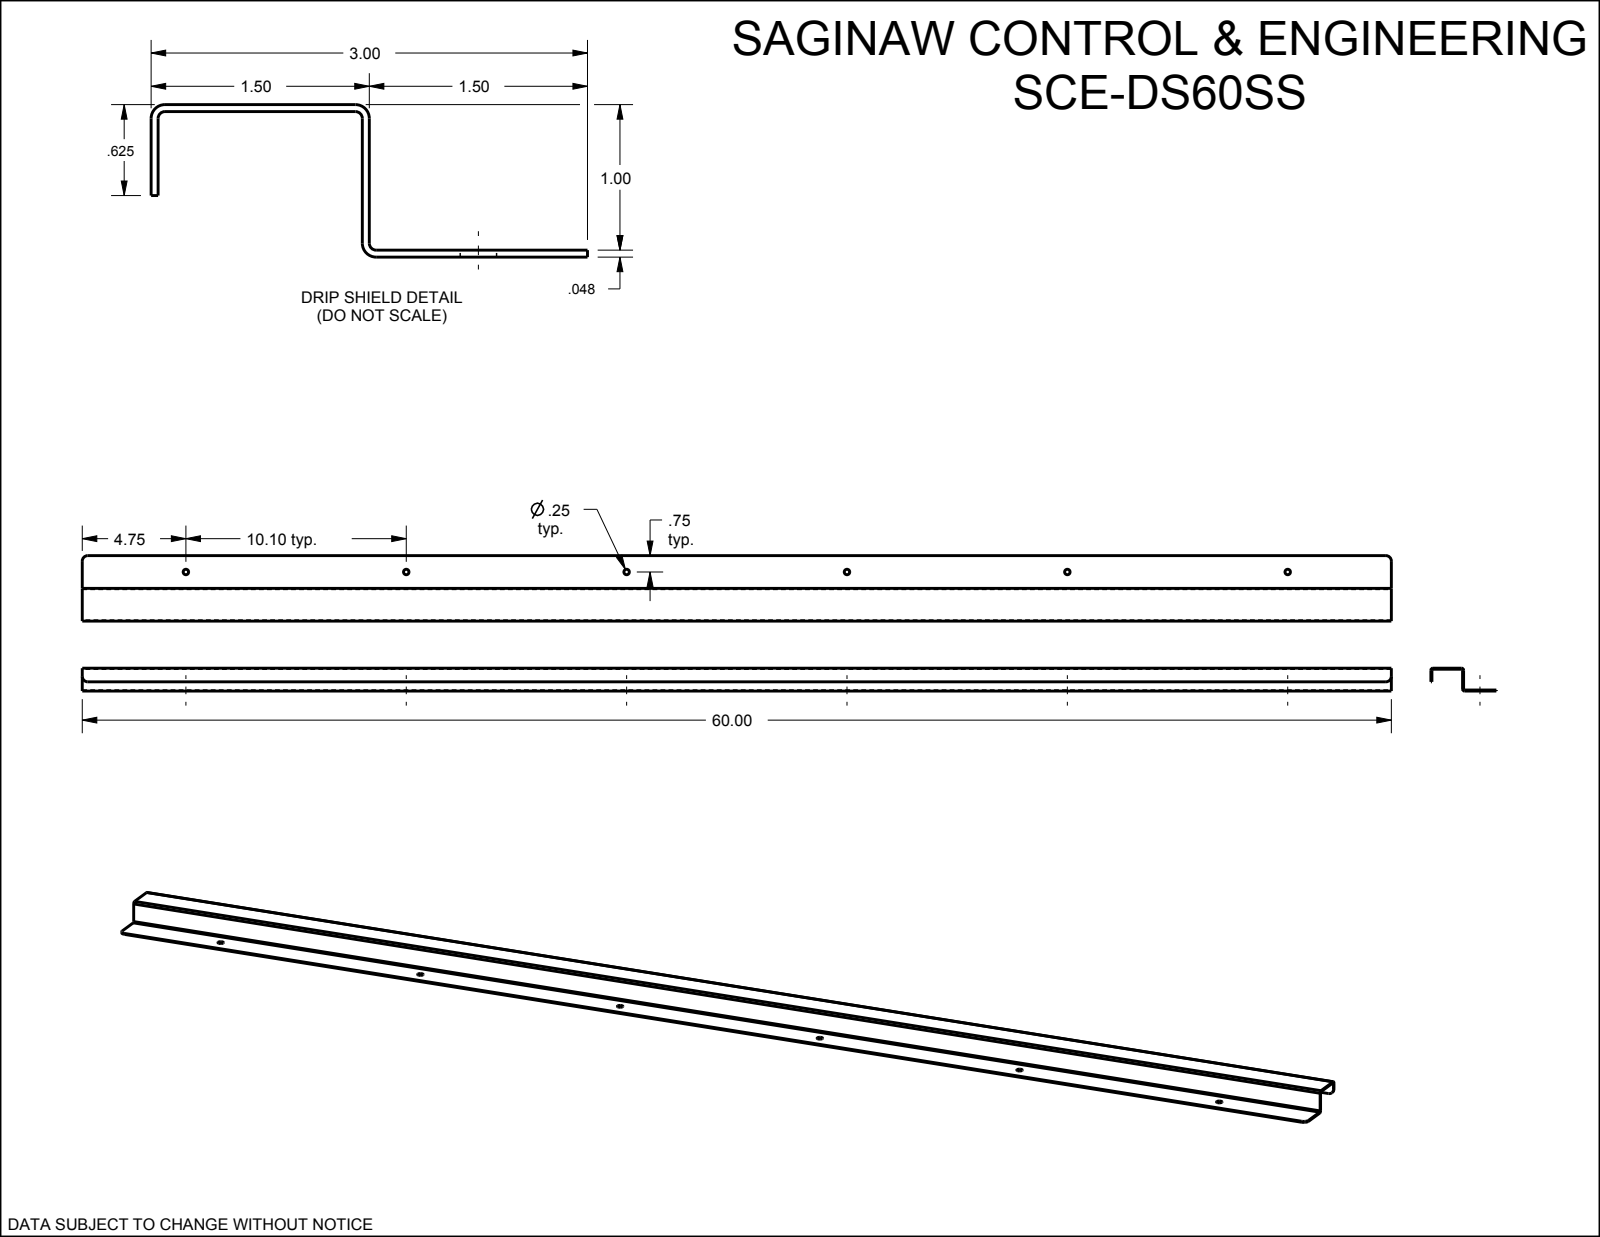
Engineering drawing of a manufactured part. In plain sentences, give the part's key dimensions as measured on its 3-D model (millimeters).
The part is named "SCE-DS60SS". Its 3-D file was written by "SolidWorks 2019 (CONFIG_CONTROL_DESIGN)". It is 1 solid with 28 faces: 12 planar, 16 cylindrical and 0 other. Overall it measures 1524 by 76.2 by 26.6 millimeters. Its volume is 211 400 cubic millimeters and its surface area 351 000 square millimeters. Round holes: 6 of diameter 6.4. Partial cylindrical surfaces (rounded edges, fillets, slot ends): 4 of radius 6.4, 3 of radius 1.2, 3 of radius 2.4. The main face-to-face distances are 1.2, 25.4, 24.2, 26.6, 36.9, 38.1, 35.7, 10.7, 9.5, 14.7. The hole center spacings are 256.5, 513.1, 769.6, 1026.2, 1282.7.
